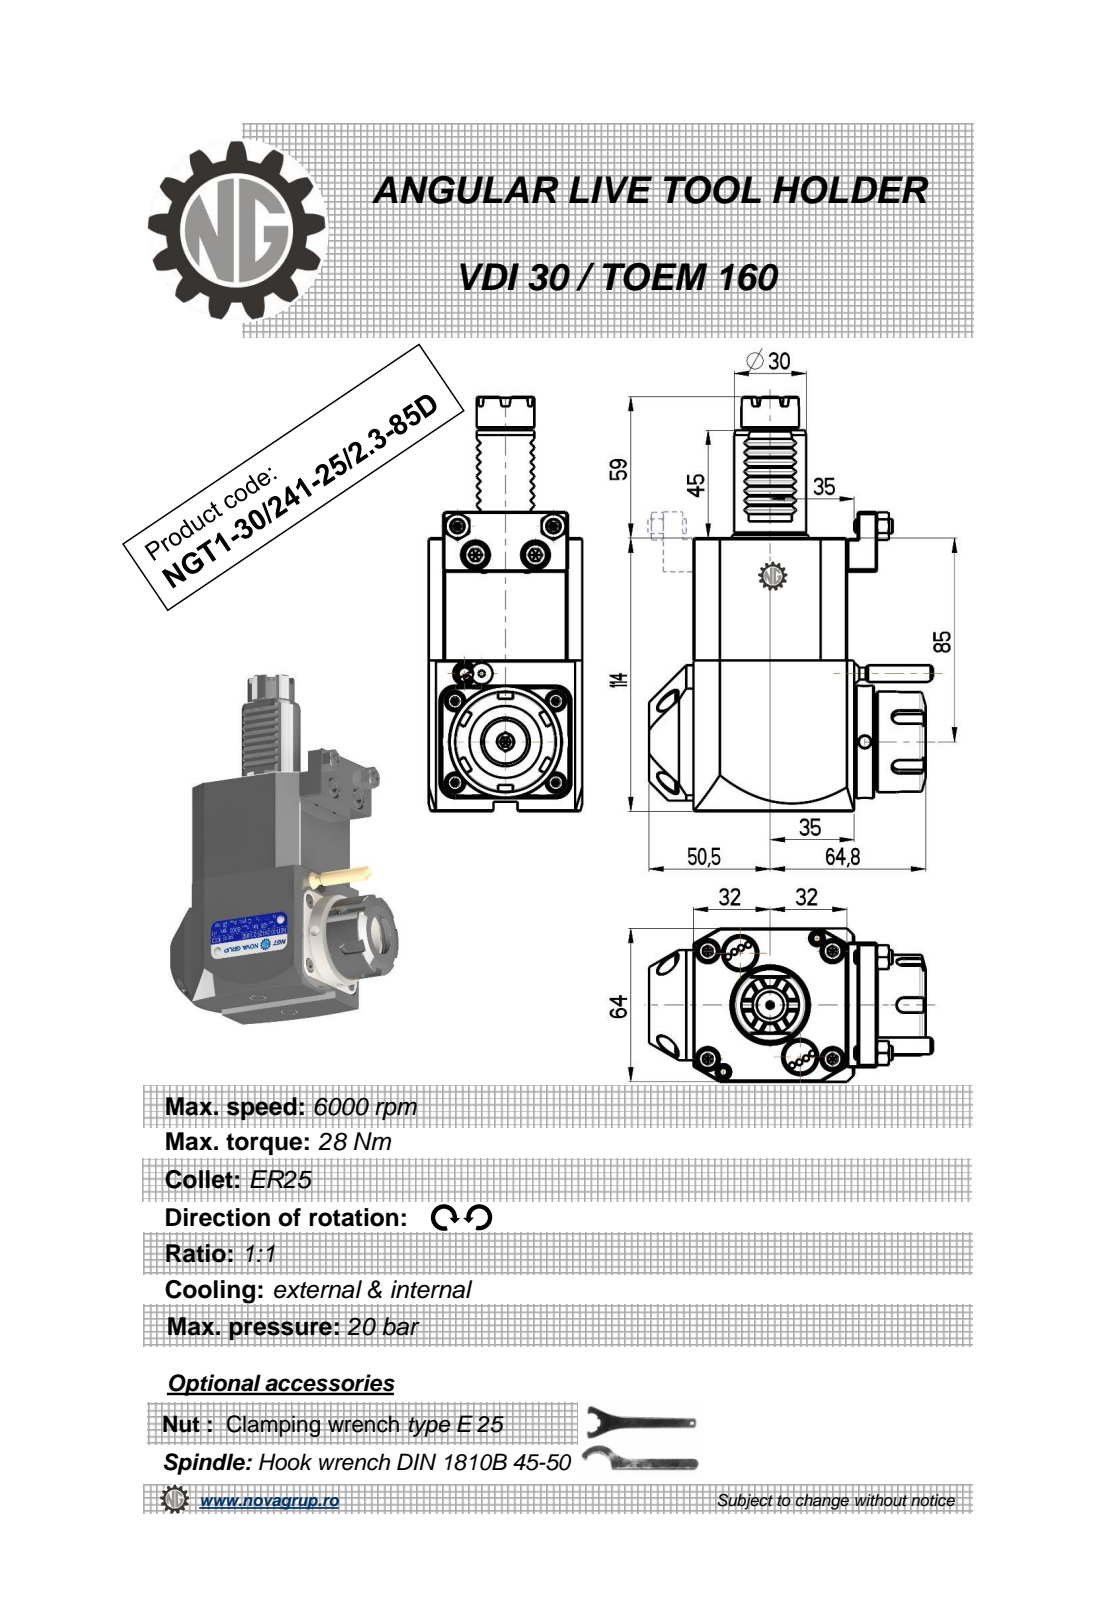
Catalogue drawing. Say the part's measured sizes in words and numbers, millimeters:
The part is named "NGT1_30_241_25_2_3_85D". Its 3-D file was written by "PRO/ENGINEER BY PARAMETRIC TECHNOLOGY CORPORATION, 2010280 (CONFIG_CONTROL_DESIGN)". It is 1 solid with 484 faces: 228 planar, 86 cylindrical and 170 other. Overall it measures 173 by 118.33 by 64 millimeters. Its volume is 585 133 cubic millimeters and its surface area 56 235 square millimeters. Round holes: 2 of diameter 5, 1 of diameter 2.5, 1 of diameter 3, 1 of diameter 20.3. Round bosses or shafts: 2 of diameter 6, 1 of diameter 47, 1 of diameter 42, 1 of diameter 35, 1 of diameter 30, 1 of diameter 24, 1 of diameter 17.7, 1 of diameter 15.2. Partial cylindrical surfaces (rounded edges, fillets, slot ends): 16 of radius 0.3, 10 of radius 0.31, 5 of radius 3, 2 of radius 160, 1 of radius 32. The main face-to-face distances are 64, 114, 3, 0.5, 9.3, 8, 3.2, 67.2, 76.42, 1.3. The hole center spacings are 33.19.
